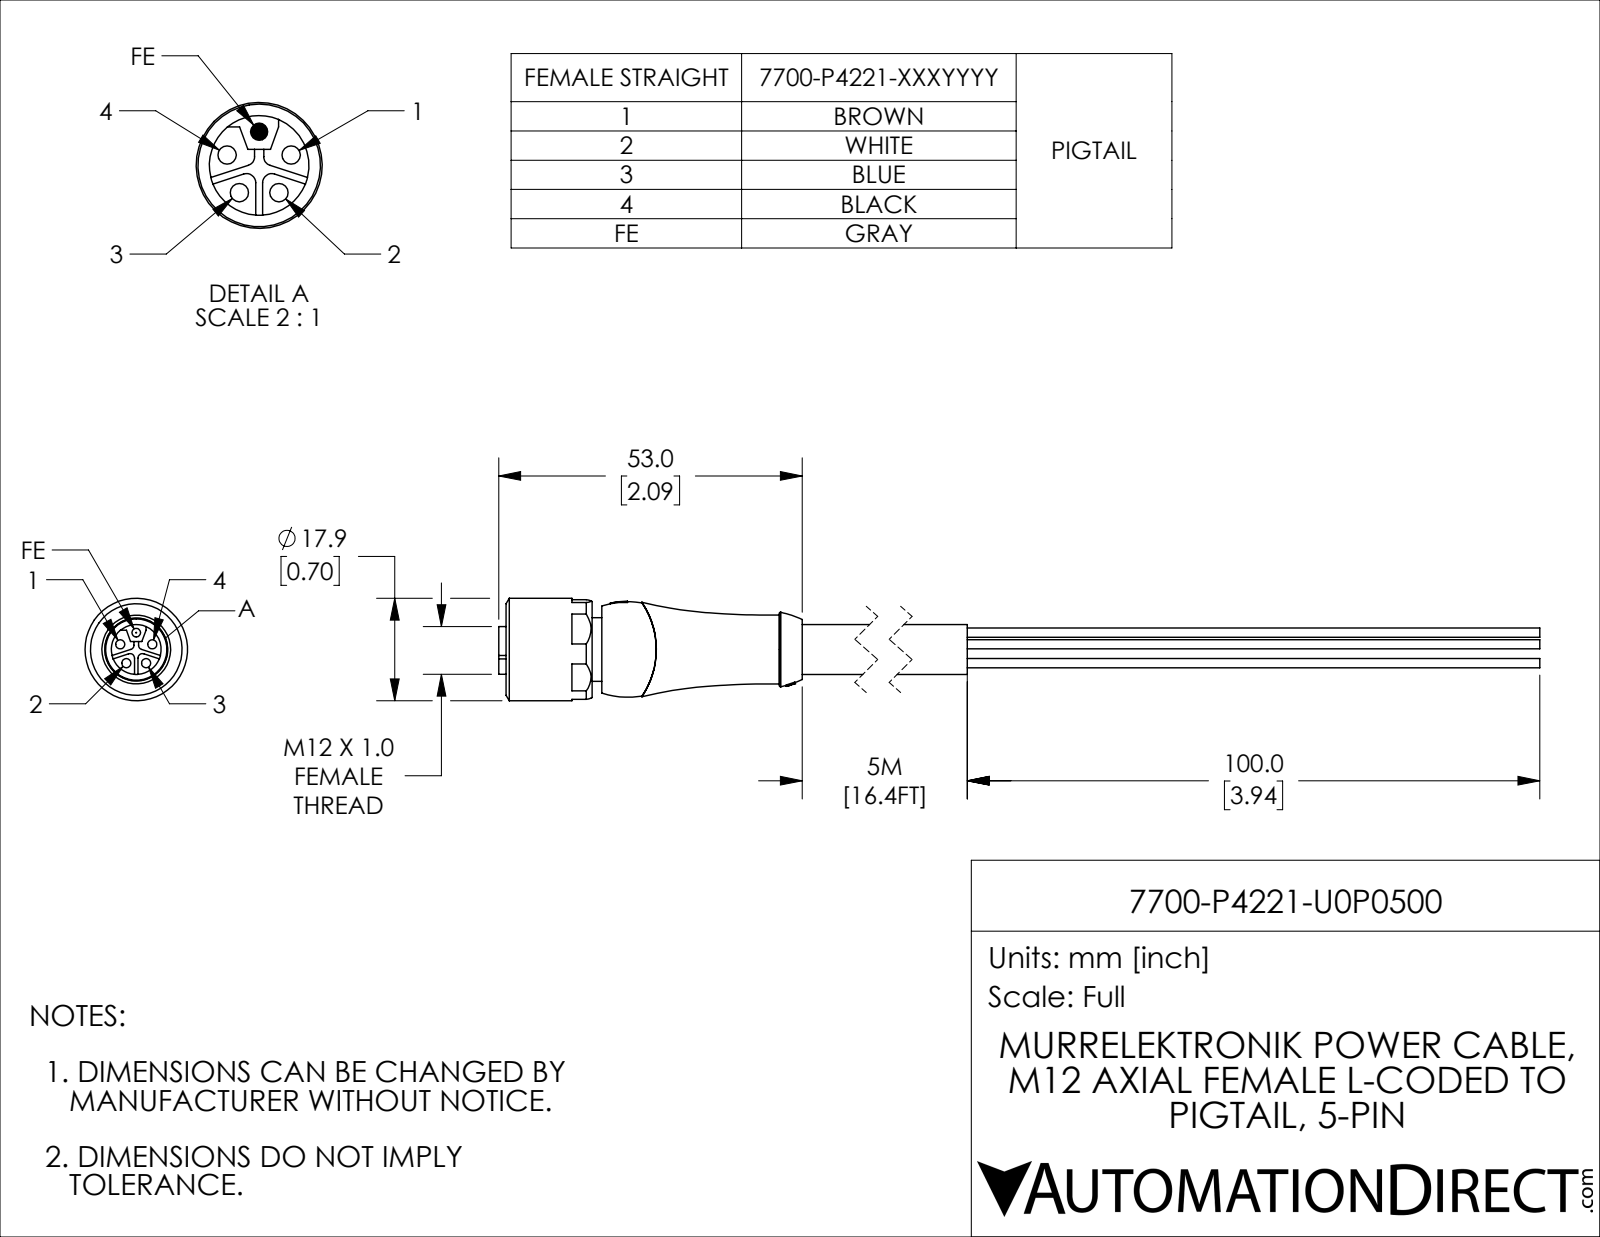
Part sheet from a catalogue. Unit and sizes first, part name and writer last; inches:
Units: inches
Overall size (bounding box): 7.598 × 0.705 × 0.705
Round holes (diameter × count): ⌀0.063 ×4, ⌀0.433 ×1, ⌀0.512 ×1
Round bosses / shafts (diameter × count): ⌀0.705 ×1, ⌀0.51 ×1, ⌀0.437 ×1, ⌀0.343 ×1, ⌀0.063 ×1, ⌀0.059 ×1
Partial cylindrical surfaces — rounded edges, fillets, slot ends (radius × count): R0.031 ×4
Main face-to-face distances: 0.657, 0.591, 0.067, 0.667, 3.61, 3.02, 2.953, 0.181, 0.362, 0.228
Hole centre spacings: 0.116, 0.136, 0.22
Volume: 0.735 in³ · Surface area: 12.83 in²
Bodies: 2 solids, 142 faces (69 planar, 40 cylindrical, 33 other)
Part name (STEP PRODUCT): 7700-P4221-U0P0500
STEP written by: SolidWorks 2021 (CONFIG_CONTROL_DESIGN)
